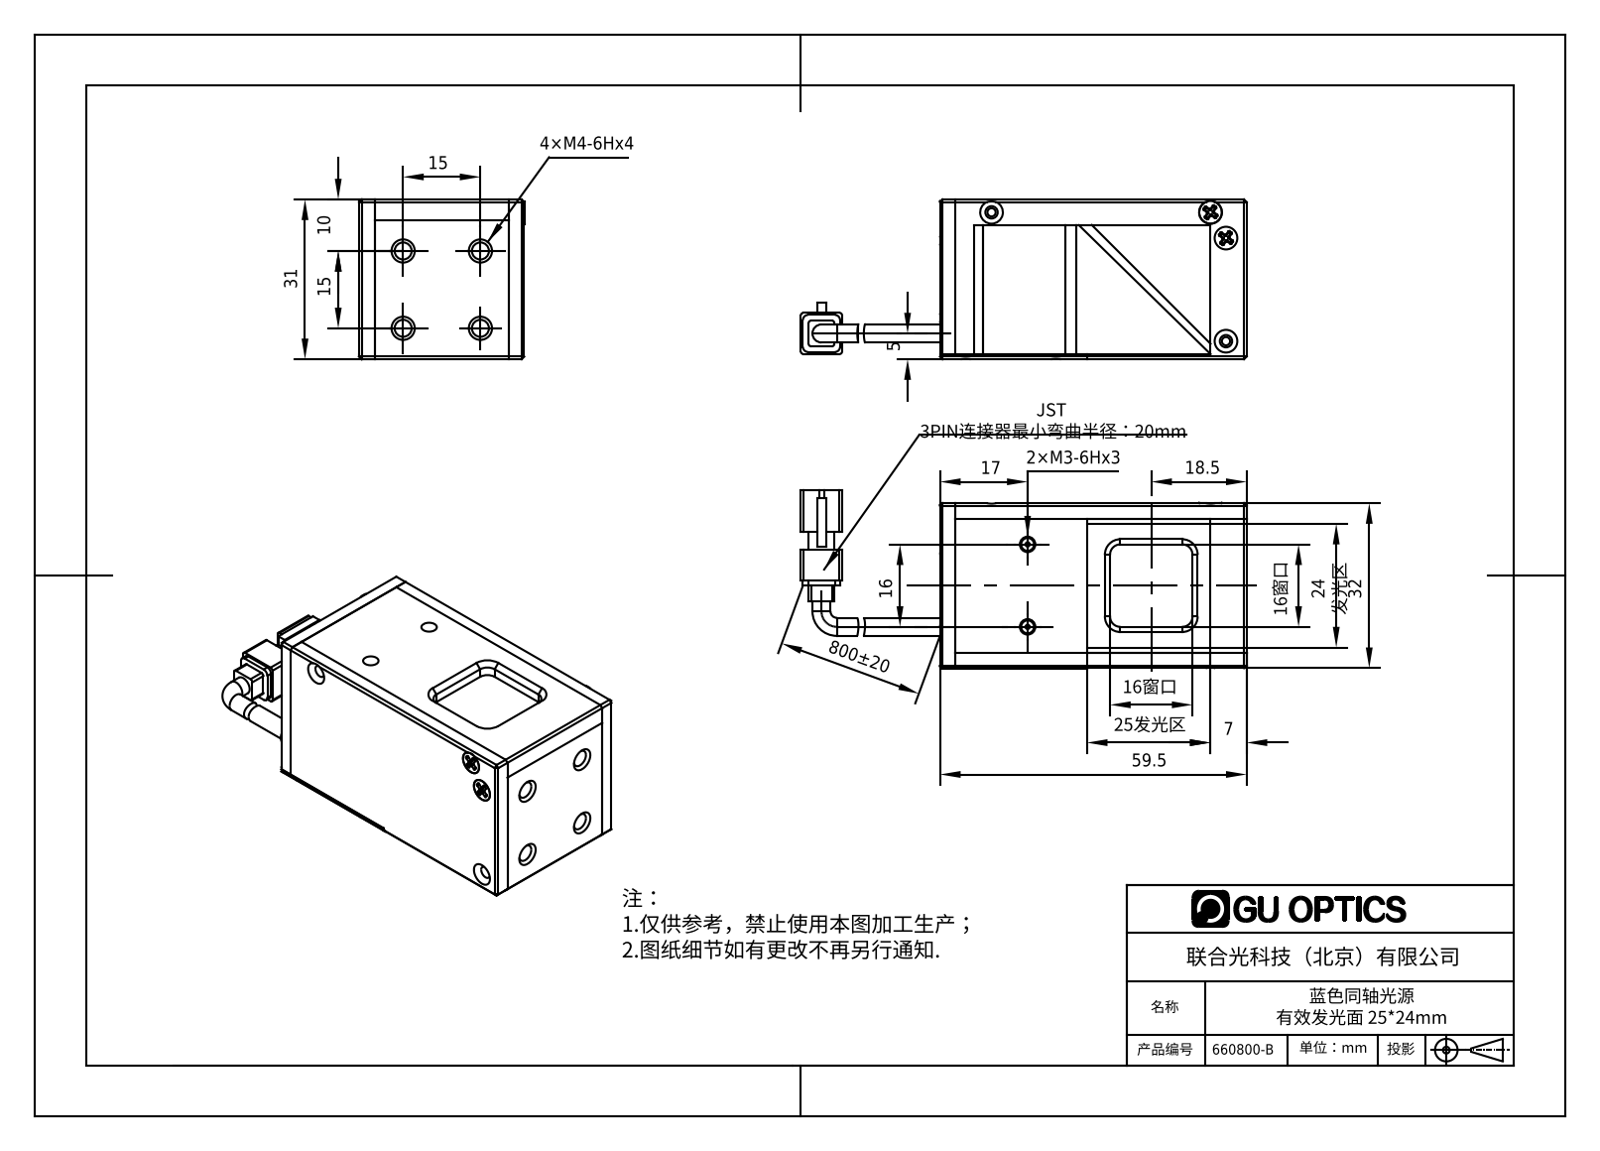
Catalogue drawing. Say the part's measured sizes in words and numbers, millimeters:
The part is named "蓝色同轴光源 有效发光面 2524mm". Its 3-D file was written by "SolidWorks 2016 (AUTOMOTIVE_DESIGN)". It is 69 solids with 1777 faces: 978 planar, 517 cylindrical and 282 other. Overall it measures 86.5 by 34.55 by 32.35 millimeters. Its volume is 34 876 cubic millimeters and its surface area 35 362 square millimeters. Round holes: 38 of diameter 3, 14 of diameter 1.6, 10 of diameter 2.4, 4 of diameter 3.3, 2 of diameter 2.5, 2 of diameter 4, 1 of diameter 5. Round bosses or shafts: 36 of diameter 3.8, 11 of diameter 2, 2 of diameter 3.5. Partial cylindrical surfaces (rounded edges, fillets, slot ends): 144 of radius 0.2, 8 of radius 0.5, 6 of radius 2, 4 of radius 1, 4 of radius 1.5, 1 of radius 1.65. The main face-to-face distances are 1, 3, 4, 28, 25, 26, 29, 24, 3.66, 2. The hole center spacings are 5.78, 9.02, 4, 12.7, 4.17, 8, 9.25, 16.53.
